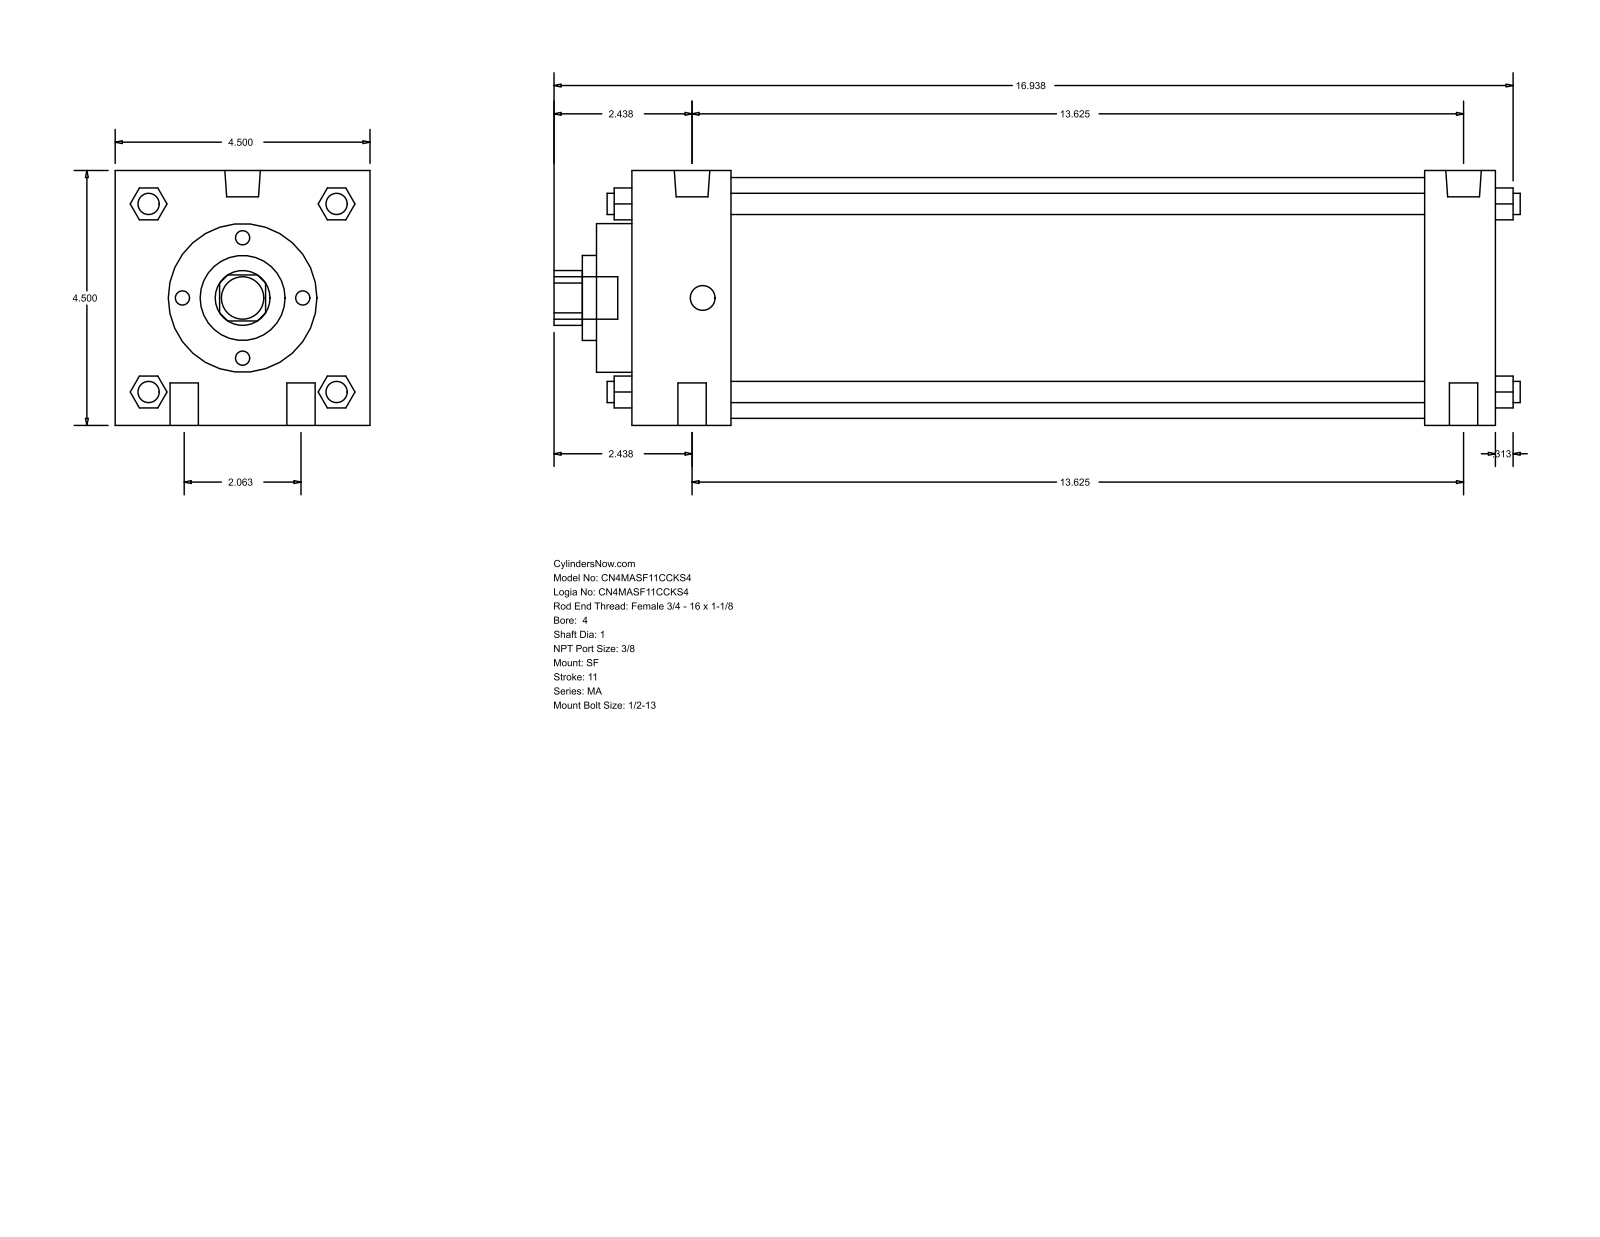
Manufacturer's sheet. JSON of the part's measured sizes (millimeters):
{"part_name": "MA_SF__0400_1", "step_written_by": "GSSL Pune (CONFIG_CONTROL_DESIGN)", "units": "millimeters", "bodies": {"solids": 0, "faces": 126, "planar": 95, "cylindrical": 31, "other": 0}, "overall_size": [433.39, 114.3, 114.3], "round_holes": [[25.4, 1], [38.1, 1], [66.67, 1], [107.95, 1]], "round_bosses_or_shafts": [[12.7, 4], [9.53, 4], [15.93, 2], [11.11, 2], [19.05, 1]], "partial_cylinders_radius": [[12.29, 1]], "face_to_face_distances": [114.3, 387.35, 355.6, 31.75, 44.46, 311.14, 342.89, 403.22, 15.87, 60.33]}
